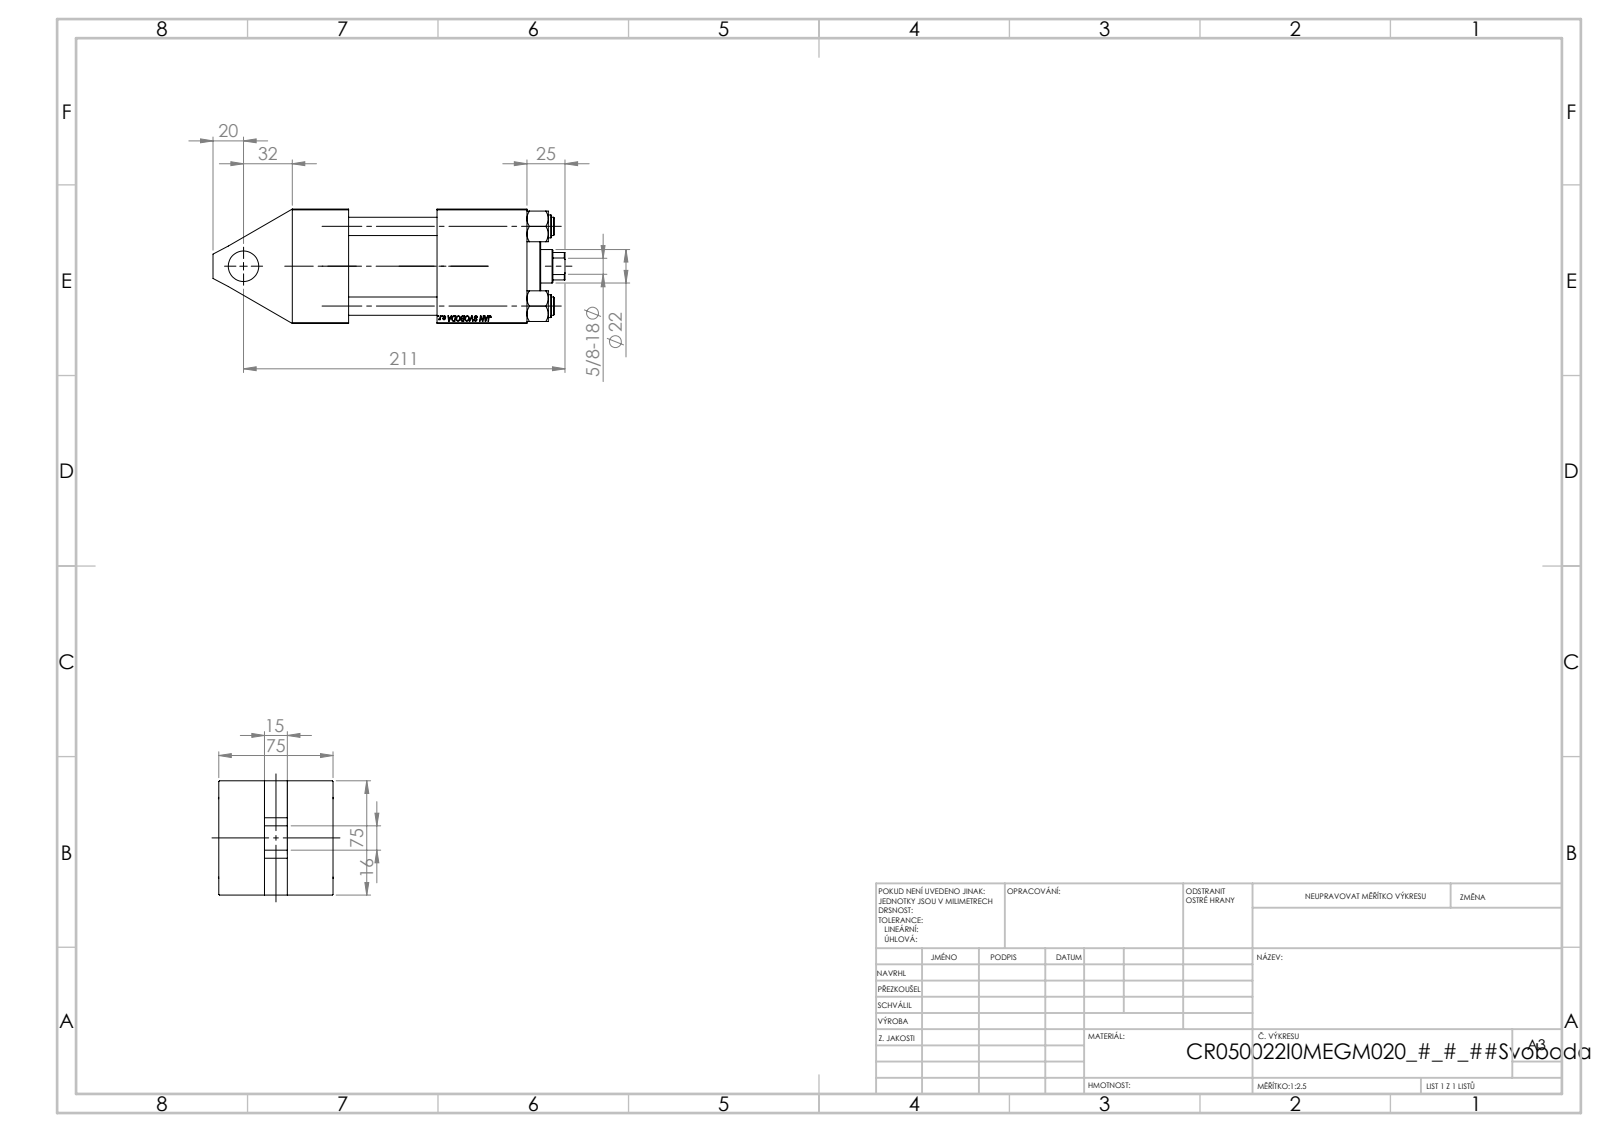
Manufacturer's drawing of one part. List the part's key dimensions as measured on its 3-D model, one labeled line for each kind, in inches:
Part name (STEP PRODUCT): V215CR_VCP_I; V215_VC_A; V215CR_I_Body; V215CR_TYCINKA_I (+1 more)
STEP written by: SolidWorks 2019 (CONFIG_CONTROL_DESIGN)
Units: inches
Bodies: 11 solids, 1078 faces (502 planar, 80 cylindrical, 496 other)
Overall size (bounding box): 9.094 × 2.974 × 2.953
Volume: 42.72 in³ · Surface area: 242.1 in²
Round holes (diameter × count): ⌀0.472 ×4, ⌀0.276 ×2, ⌀0.825 ×2, ⌀1.181 ×2, ⌀0.413 ×1, ⌀0.787 ×1, ⌀0.866 ×1, ⌀0.984 ×1, ⌀1.614 ×1, ⌀1.969 ×1, ⌀2.087 ×1
Round bosses / shafts (diameter × count): ⌀0.591 ×4, ⌀2.205 ×1, ⌀1.339 ×1
Partial cylindrical surfaces — rounded edges, fillets, slot ends (radius × count): R0.413 ×1
Main face-to-face distances: 2.953, 4.606, 1.457, 6.063, 1.772, 1.181, 3.74, 2.283, 2.323, 4.933
Hole centre spacings: 1.456, 2.059, 2.912, 3.681
